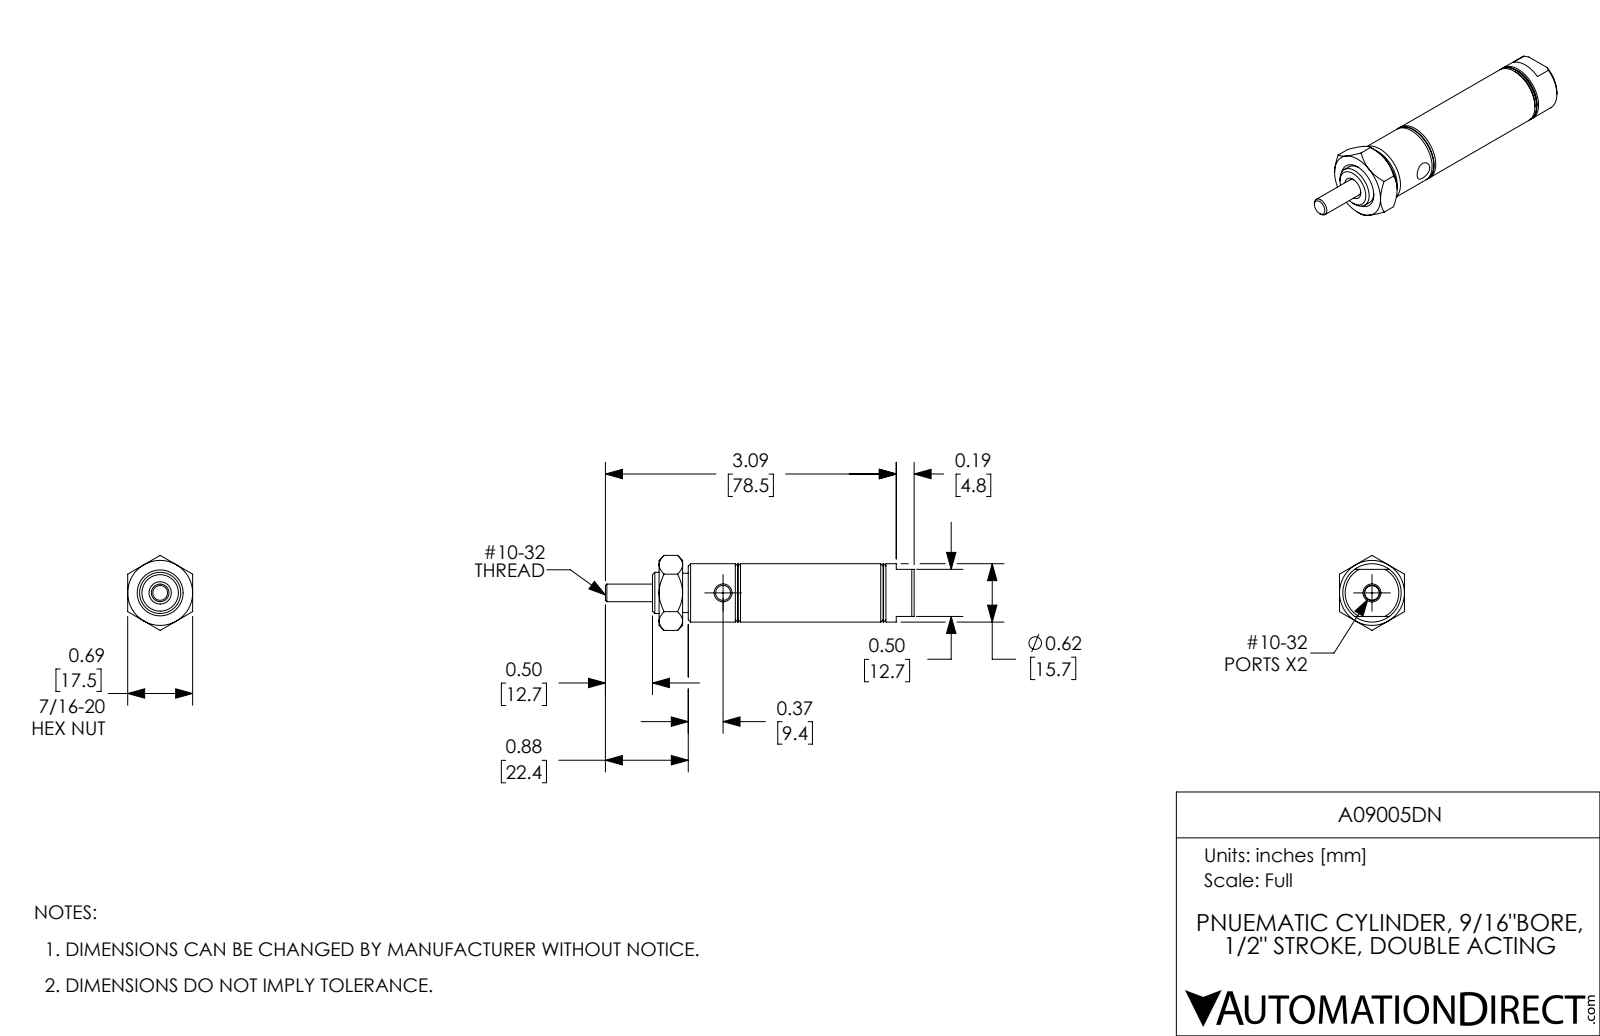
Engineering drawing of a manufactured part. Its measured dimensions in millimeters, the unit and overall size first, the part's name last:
Units: millimetres
Overall size (bounding box): 83.3 × 20.2 × 17.5
Round holes (diameter × count): ⌀4 ×2, ⌀4.8 ×2, ⌀4 ×1, ⌀4.7 ×1, ⌀11.1 ×1, ⌀14.3 ×1
Round bosses / shafts (diameter × count): ⌀15.7 ×1, ⌀10.6 ×1
Main face-to-face distances: 12.7, 17.8, 30.5, 43.2, 17.5, 25.4, 62.5, 44.7, 19.3, 32
Volume: 11 700 mm³ · Surface area: 8 503 mm²
Bodies: 3 solids, 100 faces (28 planar, 34 cylindrical, 38 other)
Part name (STEP PRODUCT): A09005DN; A09005DN_Mounting Nut_D-154; A09005DN-Rod; A09005DN-MainBody
STEP written by: SolidWorks 2017 (AUTOMOTIVE_DESIGN)
